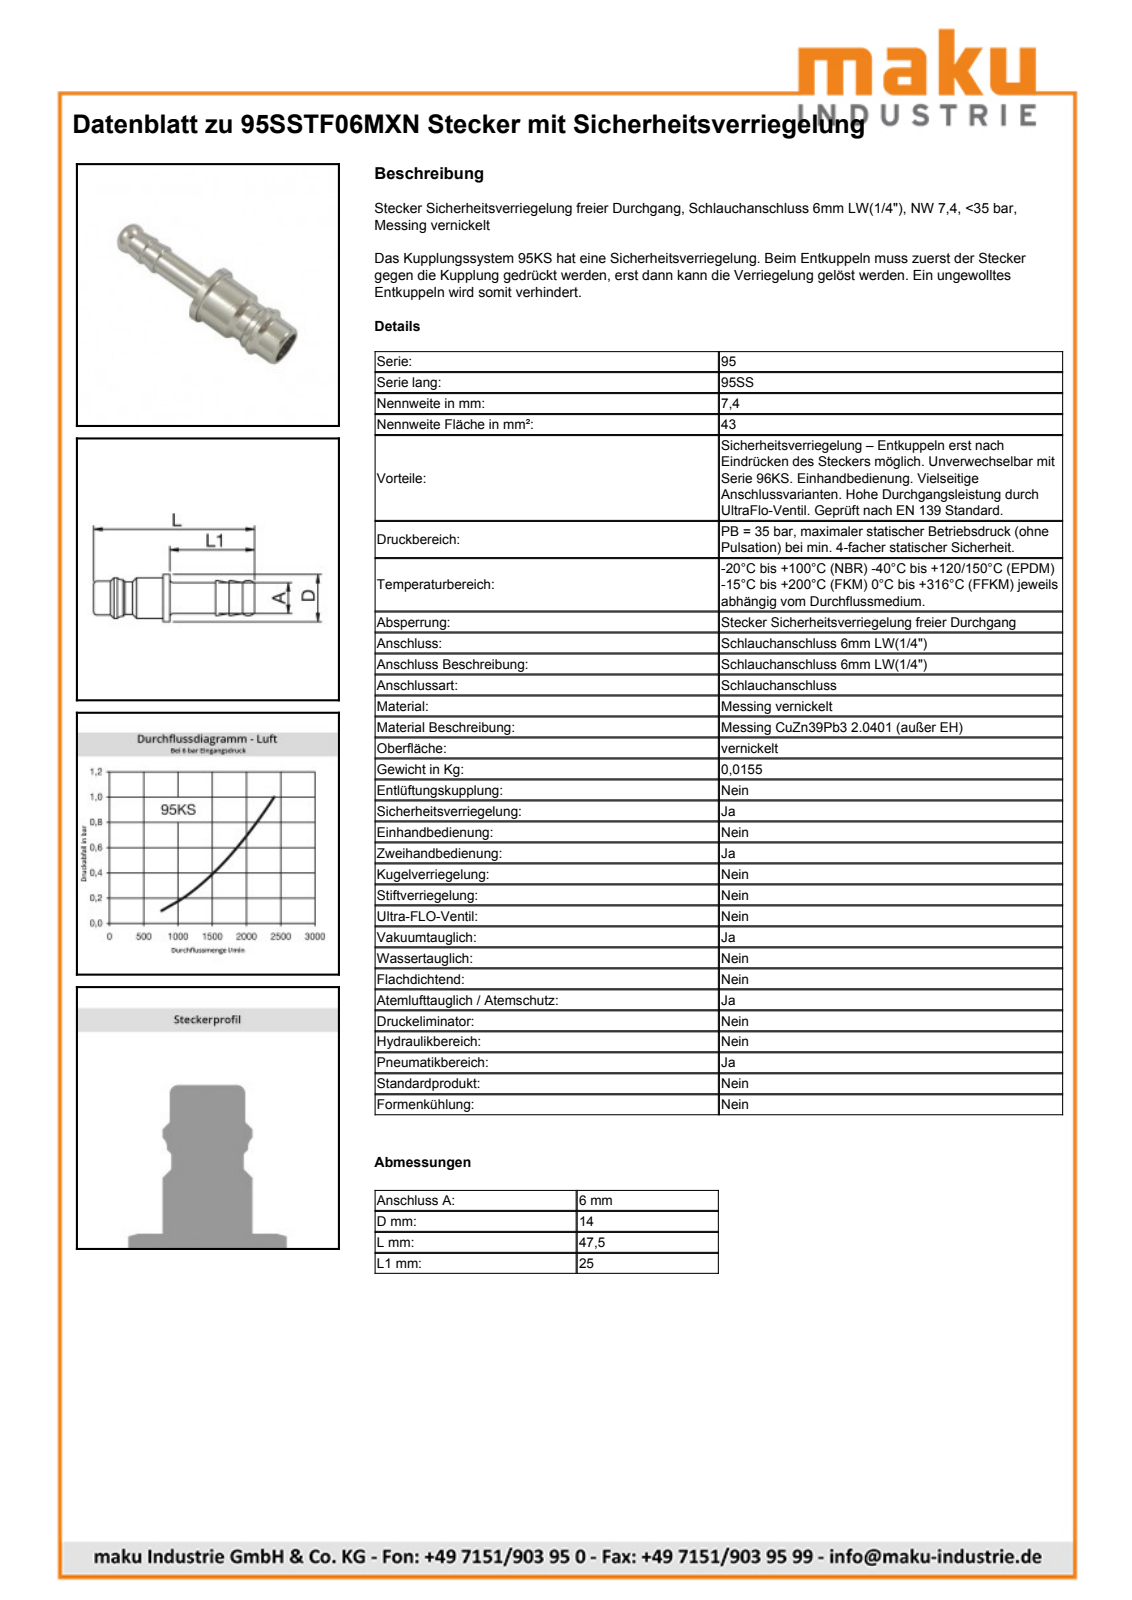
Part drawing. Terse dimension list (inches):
name: D110898
written by: Autodesk Inventor 2013 (AUTOMOTIVE_DESIGN)
unit: in
bodies: 1 solid, 30 faces (5 planar, 9 cylindrical, 16 other)
size: 1.87 × 0.551 × 0.551
volume: 0.111 in³; area: 3.711 in²
holes: 1× ⌀0.161, 1× ⌀0.291
bosses: 1× ⌀0.551, 1× ⌀0.47, 1× ⌀0.425, 1× ⌀0.39, 1× ⌀0.378, 1× ⌀0.24
face distances: 0.075, 0.984, 1.059, 1.87, 0.886, 0.811, 0.453, 0.531, 0.606, 1.417
